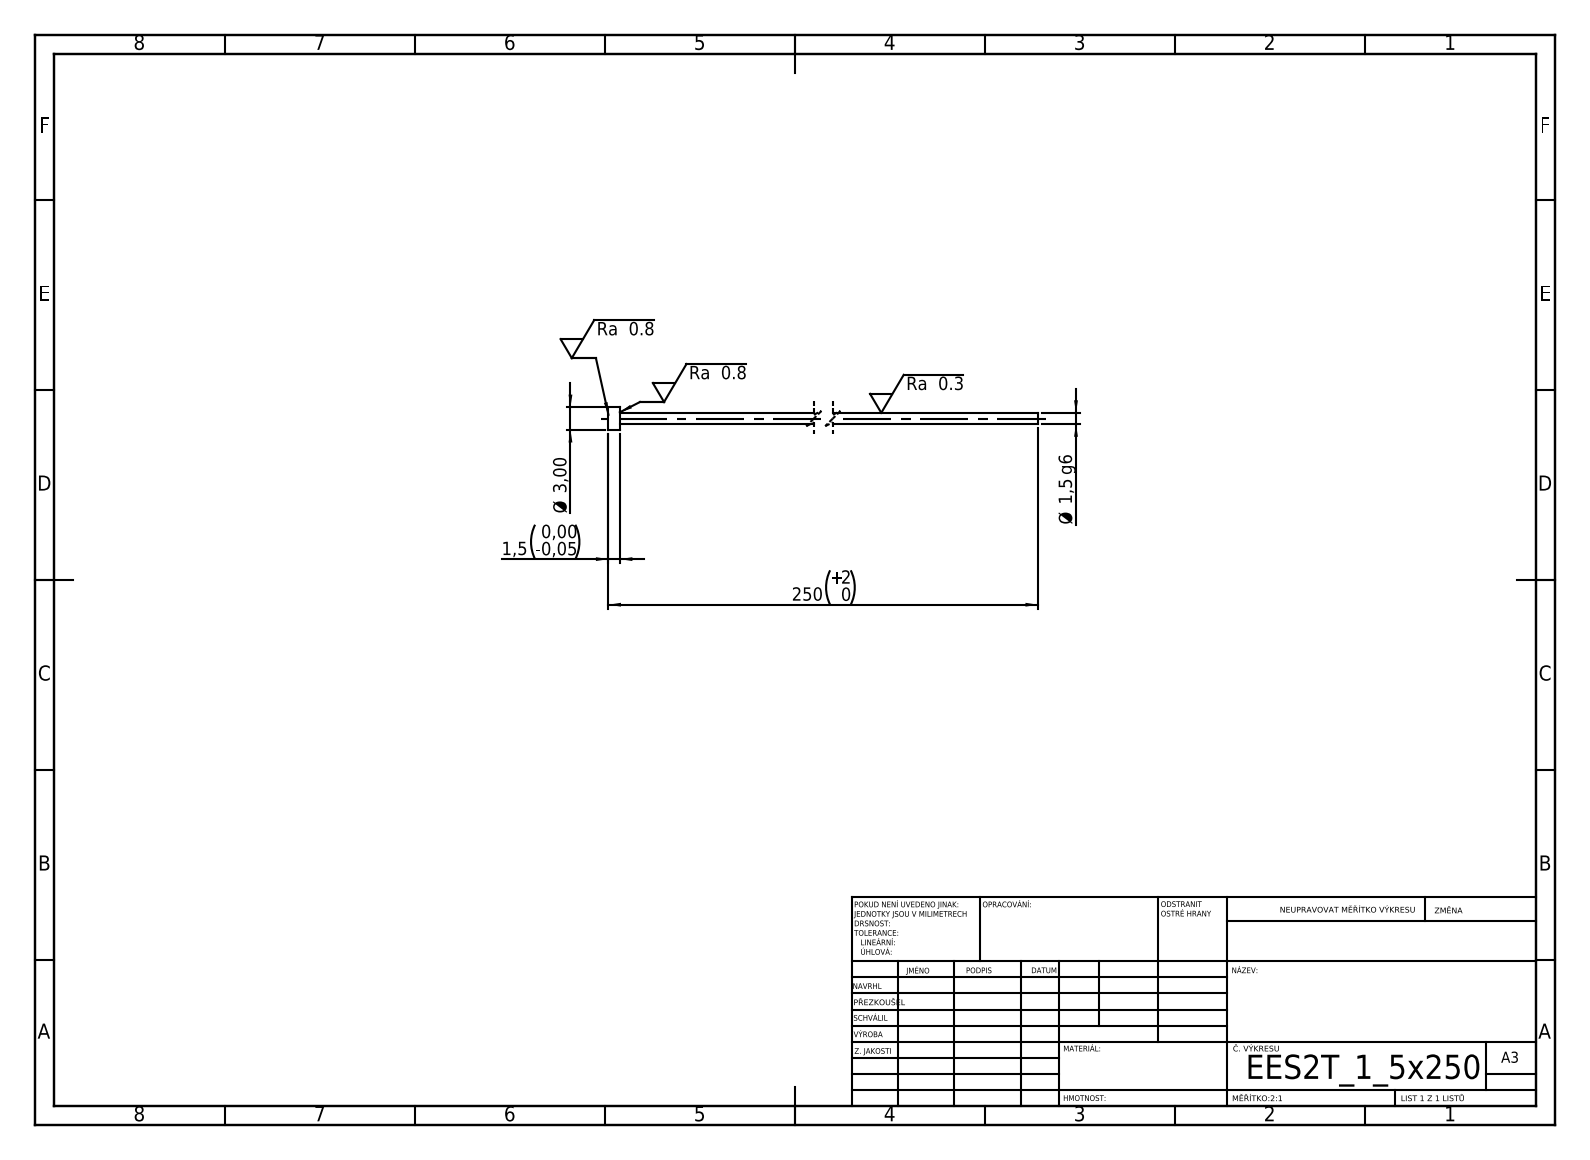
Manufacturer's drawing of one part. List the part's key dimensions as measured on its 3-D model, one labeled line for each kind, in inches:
STEP written by: SolidWorks 2019 (CONFIG_CONTROL_DESIGN)
Units: inches
Bodies: 1 solid, 7 faces (3 planar, 4 cylindrical, 0 other)
Overall size (bounding box): 9.843 × 0.118 × 0.118
Volume: 0.027 in³ · Surface area: 1.858 in²
Round bosses / shafts (diameter × count): ⌀0.118 ×1, ⌀0.059 ×1
Main face-to-face distances: 0.059, 9.843, 9.783
